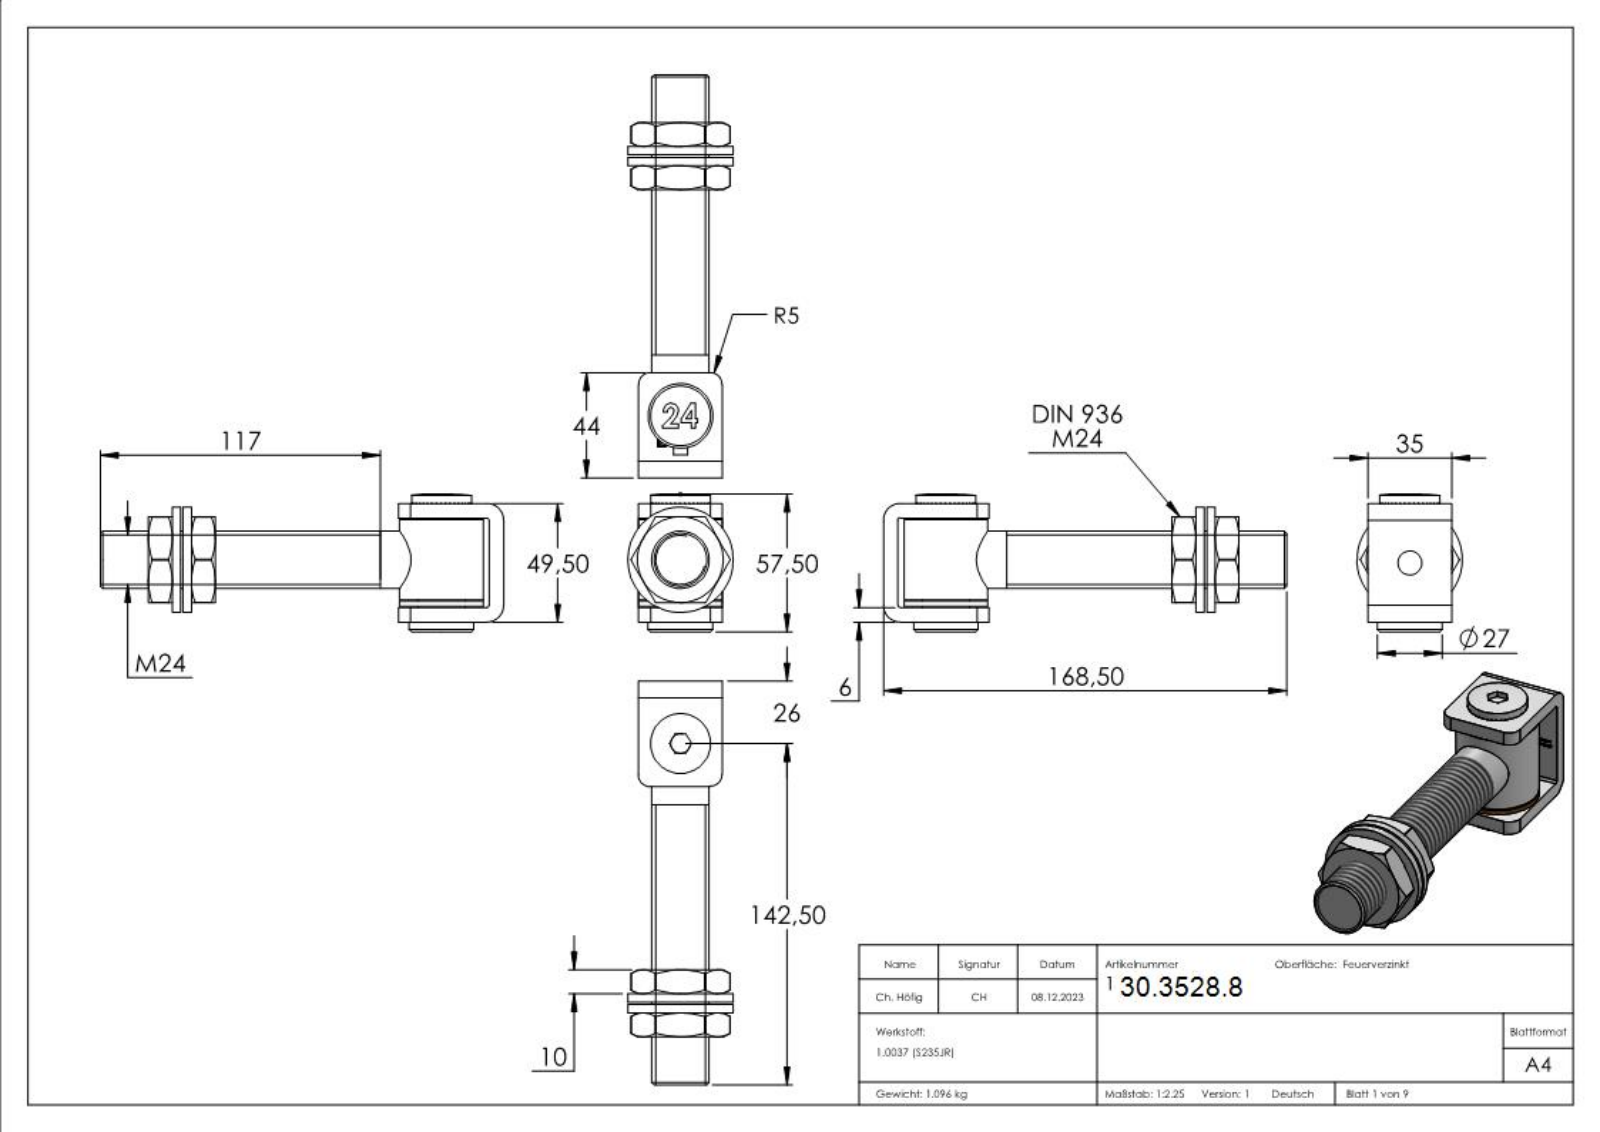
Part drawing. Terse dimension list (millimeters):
name: Torband Teil4_130-M24-FEV Teil4; Torband Teil2_130-M24-FEV Teil2; DIN 936 M8-M24_DIN 936 M24; 130-Mxx Teil6_130-M24-FEV Teil6 (+4 more)
written by: SolidWorks 2018 (CONFIG_CONTROL_DESIGN)
unit: mm
bodies: 9 solids, 597 faces (400 planar, 39 cylindrical, 158 other)
size: 168.5 × 57.45 × 44
volume: 140 367 mm³; area: 47 533 mm²
holes: 1× ⌀8.5, 1× ⌀10, 1× ⌀20.5, 1× ⌀20.6, 1× ⌀21, 1× ⌀26
bosses: 1× ⌀44, 1× ⌀35, 1× ⌀27, 1× ⌀25, 1× ⌀24, 1× ⌀19.7, 1× ⌀10
rounds: 6× R0.5, 2× R1, 2× R5, 2× R7
face distances: 6, 4.5, 3.5, 43.5, 10, 8, 124.5, 14.5, 13.5, 18
hole spacings: 1.33
